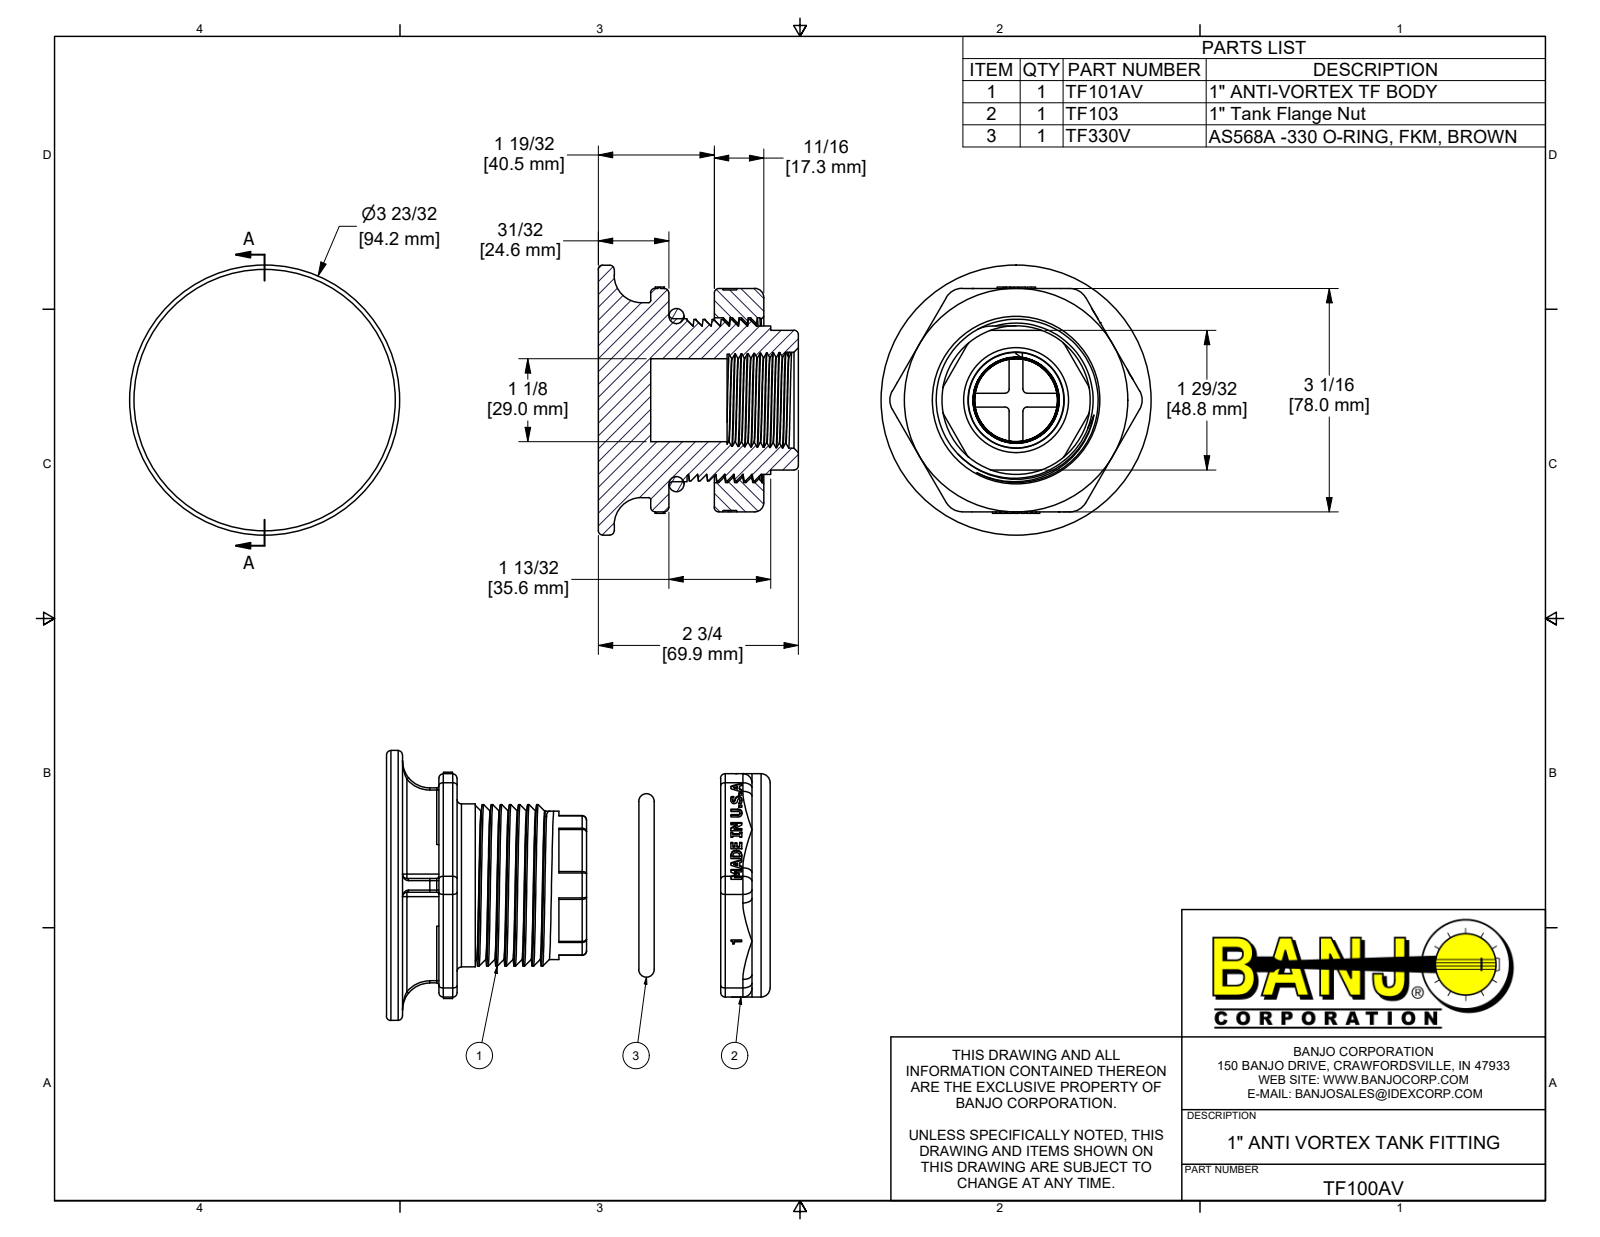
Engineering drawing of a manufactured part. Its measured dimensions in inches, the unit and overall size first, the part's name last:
Units: inches
Overall size (bounding box): 3.71 × 3.71 × 2.75
Round holes (diameter × count): ⌀1.14 ×1, ⌀2.12 ×1, ⌀2.265 ×1
Round bosses / shafts (diameter × count): ⌀3.71 ×1, ⌀3.07 ×1, ⌀2.24 ×1, ⌀2.22 ×1, ⌀2.04 ×1
Partial cylindrical surfaces — rounded edges, fillets, slot ends (radius × count): R0.06 ×38, R0.03 ×16, R0.062 ×6, R0.125 ×6, R0.25 ×6, R0.375 ×4, R0.5 ×1, R0.639 ×1
Main face-to-face distances: 0.22, 0.5, 0.72, 0.25, 1.595, 1.375, 0.875, 0.97, 0.75, 0.625
Volume: 11.81 in³ · Surface area: 98.31 in²
Bodies: 3 solids, 852 faces (480 planar, 131 cylindrical, 241 other)
Part name (STEP PRODUCT): TF100AV; TF101AV; TF103; TF103X (+1 more)
STEP written by: Autodesk Inventor 2019 (AUTOMOTIVE_DESIGN)
